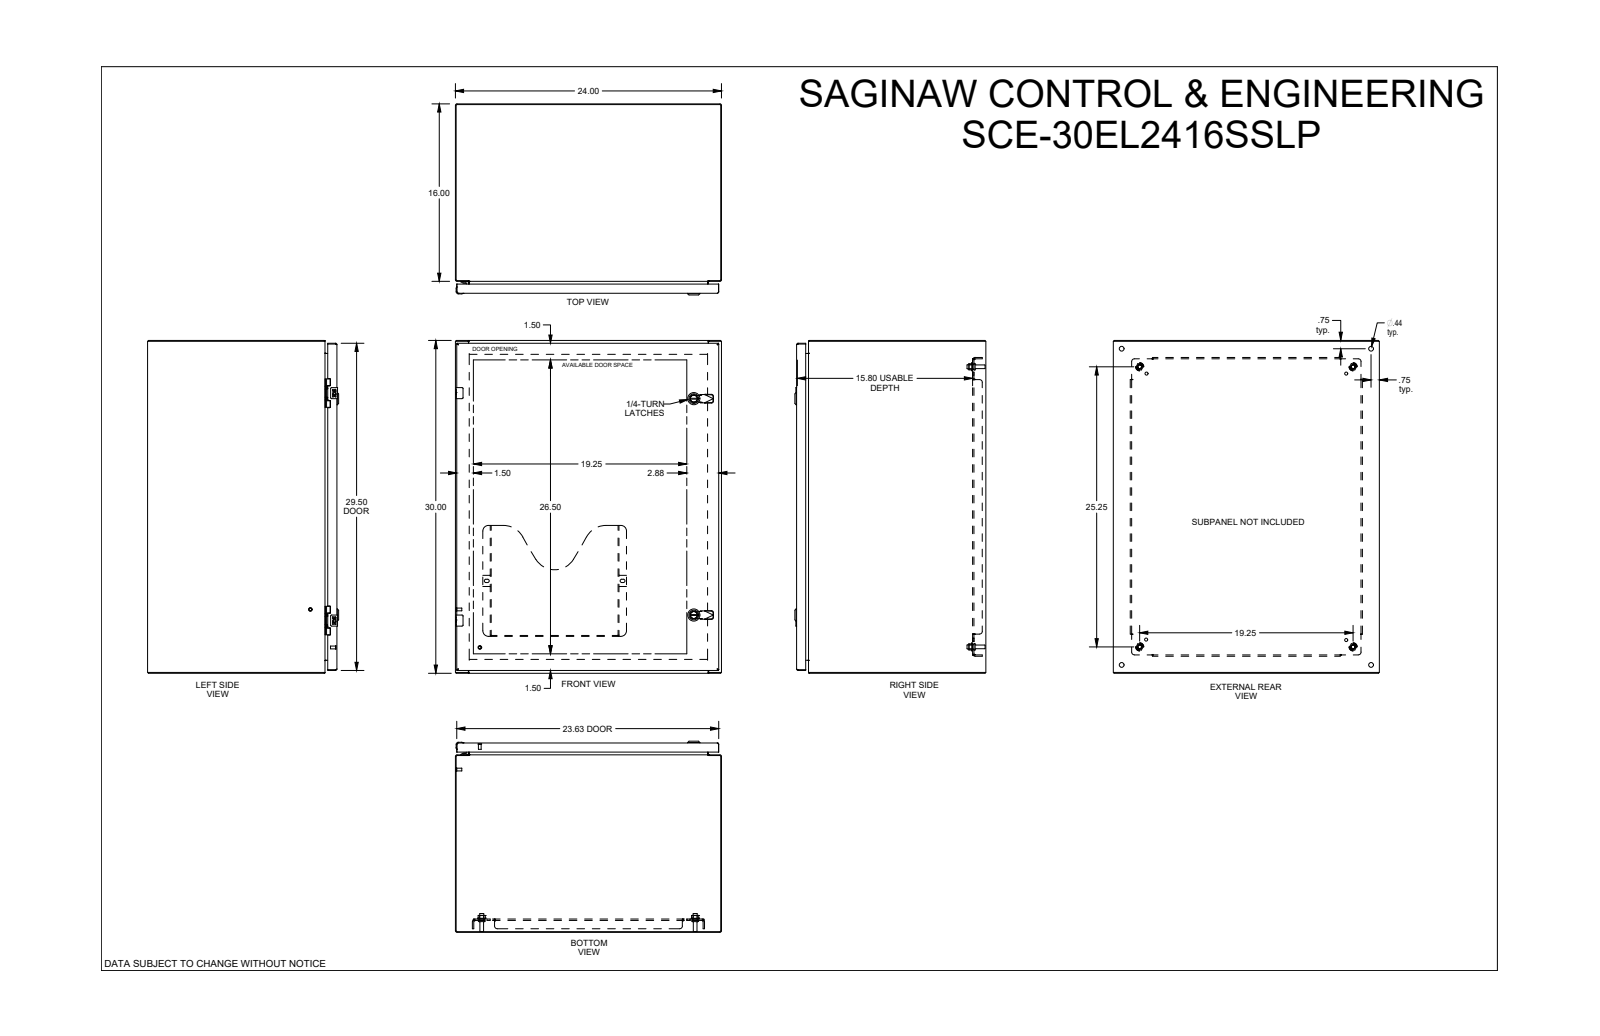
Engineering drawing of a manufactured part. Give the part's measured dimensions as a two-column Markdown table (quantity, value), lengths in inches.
| quantity | value |
| --- | --- |
| part name | SCE-30EL2416SSLP |
| STEP written by | SolidWorks 2019 (CONFIG_CONTROL_DESIGN) |
| units | inches |
| bodies | 0 solids, 2838 faces (1307 planar, 759 cylindrical, 772 other) |
| overall size | 30 × 24 × 17.23 |
| round holes (diameter × count) | 0.172 × 4, 0.205 × 4, 0.244 × 4, 0.266 × 4, 0.281 × 4, 0.367 × 4, 0.437 × 4, 0.5 × 4, 0.375 × 3, 0.156 × 2, 0.197 × 2, 0.218 × 2 |
| round bosses / shafts (diameter × count) | 0.17 × 6, 0.366 × 4, 0.332 × 4, 0.25 × 4, 0.248 × 4, 0.196 × 3, 1.102 × 2, 0.866 × 2 |
| partial cylindrical surfaces (radius × count) | 0.012 × 56, 0.015 × 32, 0.01 × 28, 0.04 × 23, 0.02 × 20, 0.029 × 12, 0.07 × 10, 0.145 × 10 |
| main face-to-face distances | 0.075, 23.925, 0.075, 29.925, 16.998, 16.923, 17.073, 16.998, 1.2, 15.873 |
| hole center spacings | 20.5, 0.985, 0.02, 0.875, 4.493, 20.938, 3.173, 18.641 |
